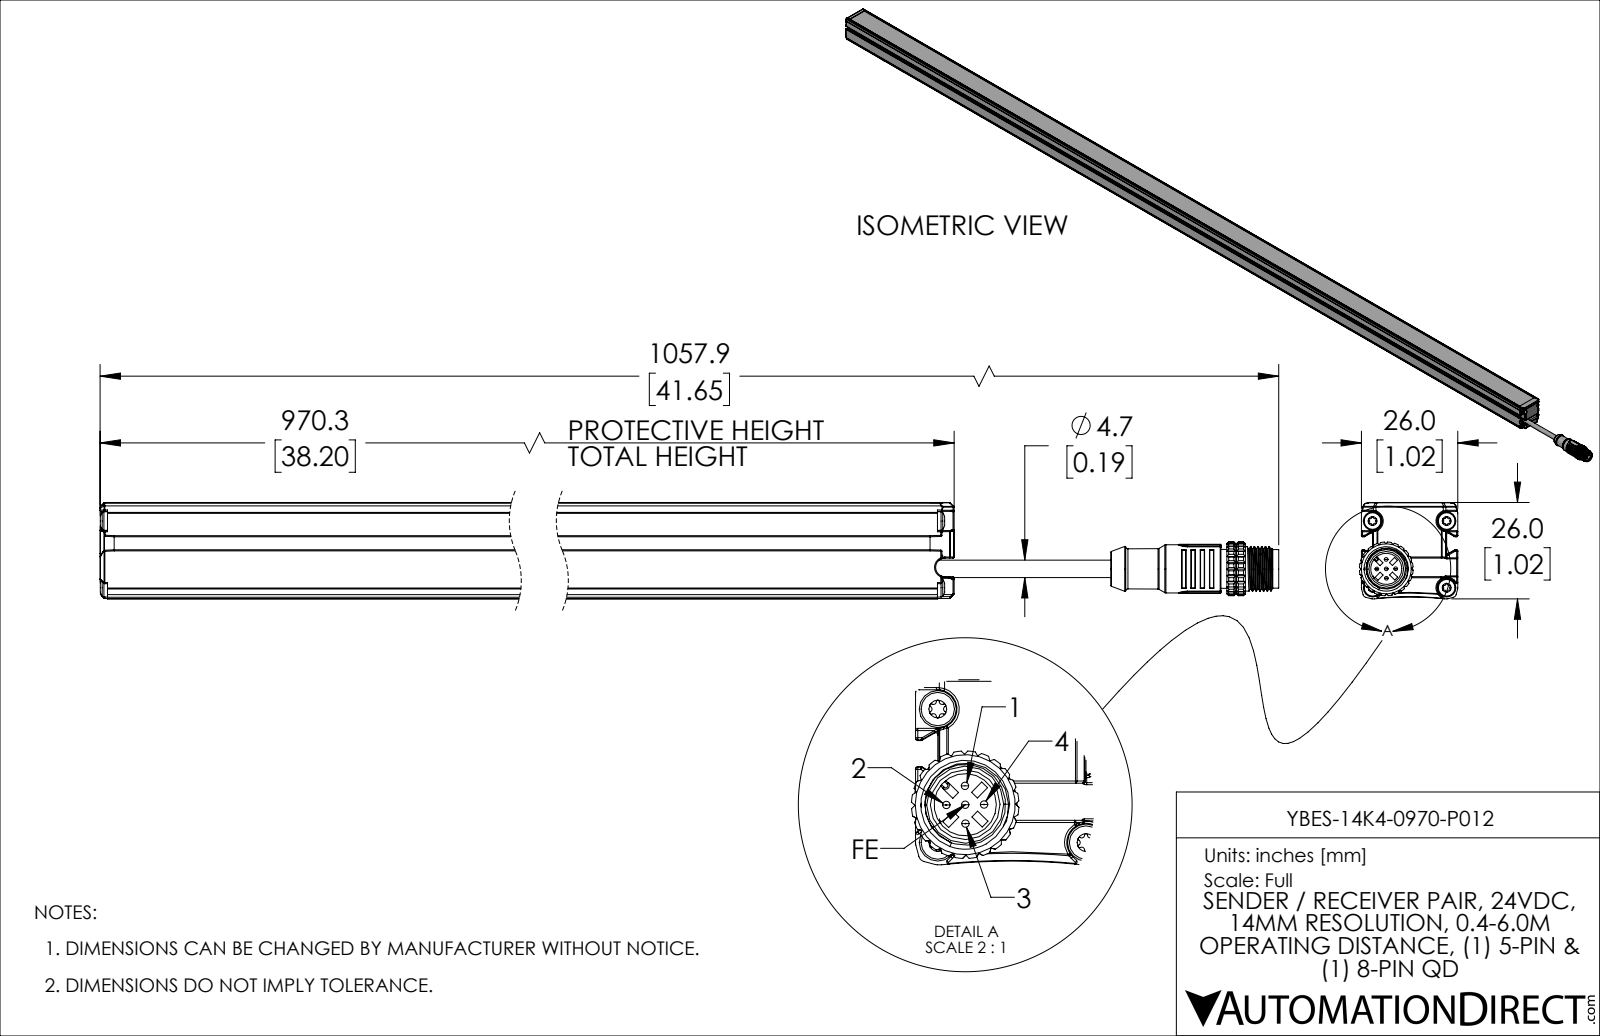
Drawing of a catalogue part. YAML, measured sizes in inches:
part_name: "YBES-14K4-0970-P012_REV1"
step_written_by: "SolidWorks 2019 (AUTOMOTIVE_DESIGN)"
units: inches
bodies: {solids: 2, faces: 1741, planar: 547, cylindrical: 719, other: 475}
overall_size: [41.65, 1.045, 1.024]
volume: 13.88
surface_area: 384.6
round_holes:
  - {diameter: 0.094, count: 4}
  - {diameter: 0.1, count: 4}
  - {diameter: 0.146, count: 4}
  - {diameter: 0.197, count: 4}
  - {diameter: 0.189, count: 1}
  - {diameter: 0.232, count: 1}
  - {diameter: 0.331, count: 1}
round_bosses_or_shafts:
  - {diameter: 0.039, count: 5}
  - {diameter: 0.126, count: 4}
  - {diameter: 0.098, count: 4}
  - {diameter: 0.051, count: 4}
  - {diameter: 0.059, count: 2}
  - {diameter: 0.531, count: 1}
  - {diameter: 0.512, count: 1}
  - {diameter: 0.472, count: 1}
partial_cylinders:
  - {radius: 0.008, count: 153}
  - {radius: 0.012, count: 115}
  - {radius: 0.008, count: 24}
  - {radius: 0.015, count: 24}
  - {radius: 0.039, count: 18}
  - {radius: 0.016, count: 16}
  - {radius: 0.006, count: 10}
  - {radius: 0.02, count: 7}
face_to_face_distances: [0.118, 0.059, 0.071, 0.835, 1.024, 0.717, 0.047, 0.016, 0.906, 0.189]
hole_center_spacings: [0.709, 0.787, 1.059, 0.248, 0.528, 0.672, 0.819]
